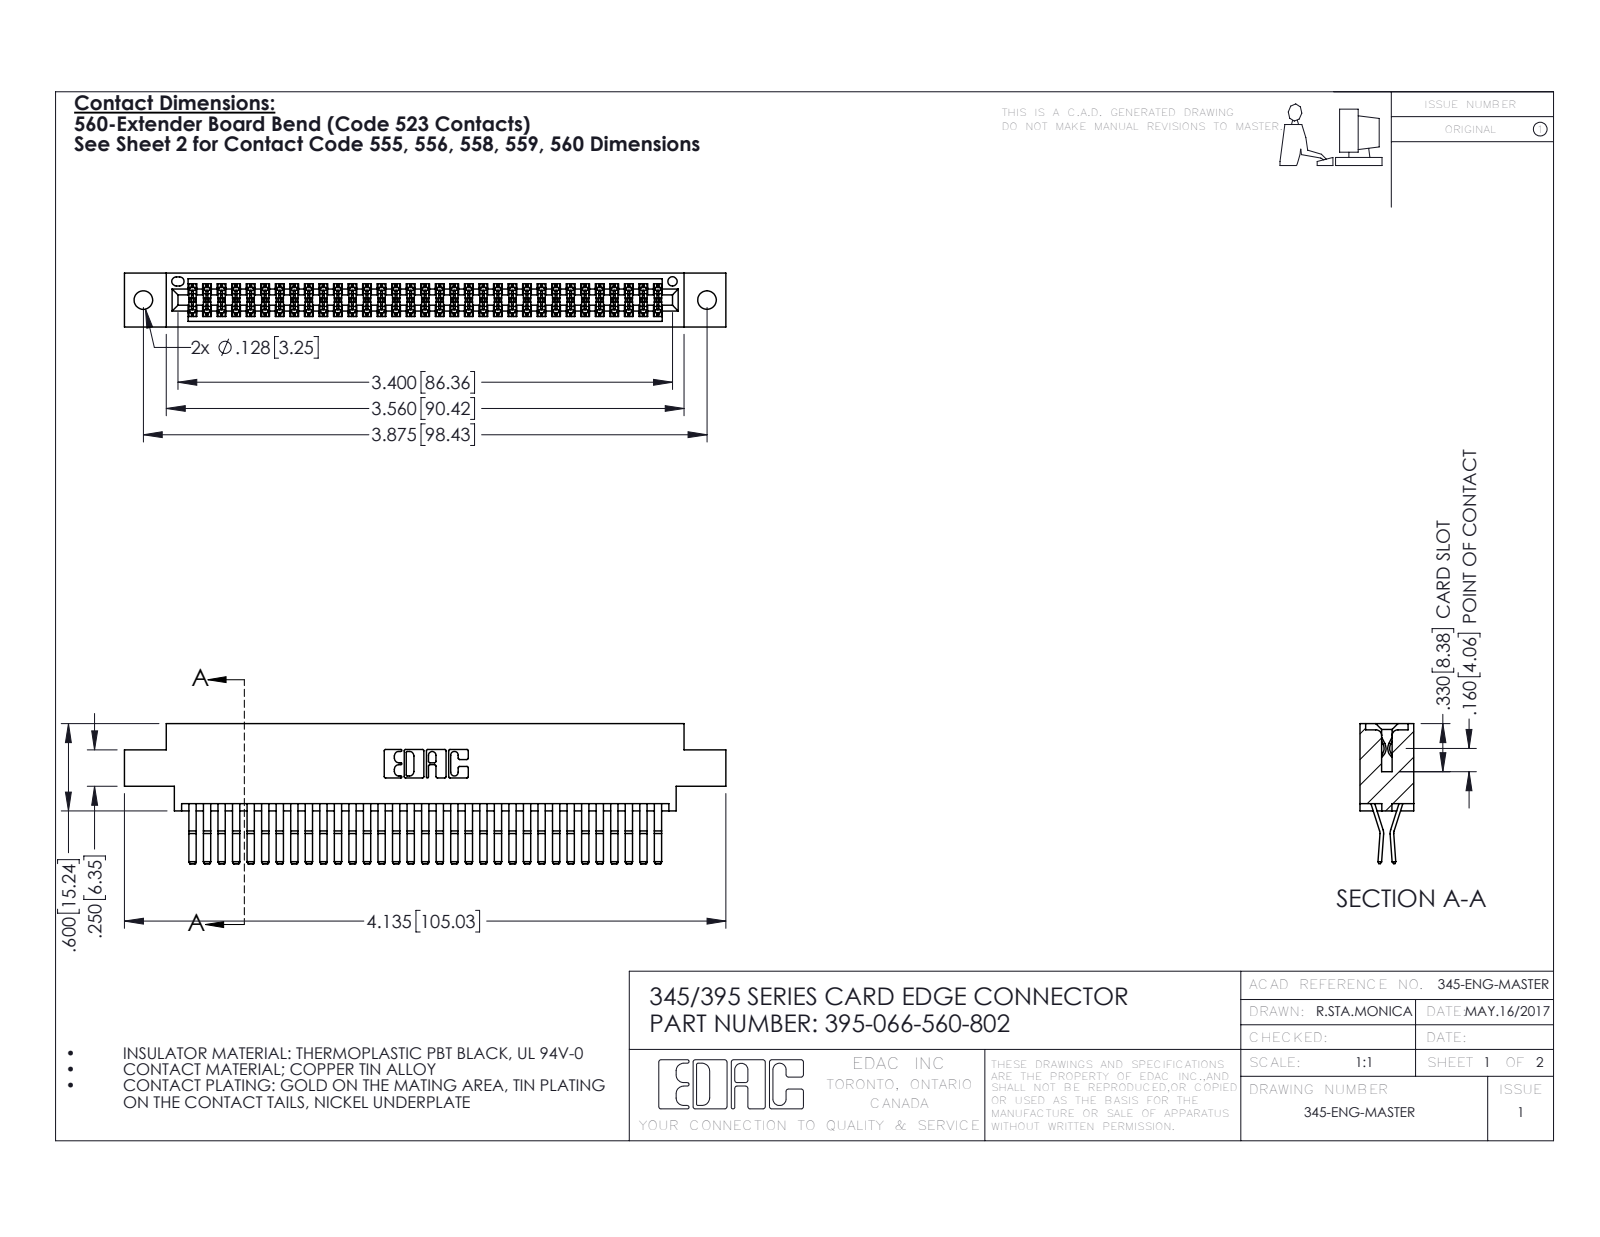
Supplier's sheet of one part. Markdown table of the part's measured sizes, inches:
| quantity | value |
| --- | --- |
| part name | 345-292-001_560 Tail; 395-066-560-802; 345 Part_0.170 Offset - 0.128 Dia |
| STEP written by | SolidWorks 2016 (CONFIG_CONTROL_DESIGN) |
| units | inches |
| bodies | 67 solids, 3562 faces (2262 planar, 1300 cylindrical, 0 other) |
| overall size | 4.135 × 0.962 × 0.37 |
| volume | 0.635 in³ |
| surface area | 25.09 in² |
| round holes (diameter × count) | 0.128 × 2, 0.064 × 1 |
| partial cylindrical surfaces (radius × count) | 0.006 × 100, 0.01 × 22, 0.007 × 6, 0.031 × 6, 0.026 × 3, 0.01 × 2, 0.014 × 2, 0.019 × 2 |
| main face-to-face distances | 0.025, 0.298, 0.072, 0.37, 0.2, 0.098, 0.272, 0.225, 0.175, 0.149 |
| hole center spacings | 0.27, 3.64, 3.875 |
